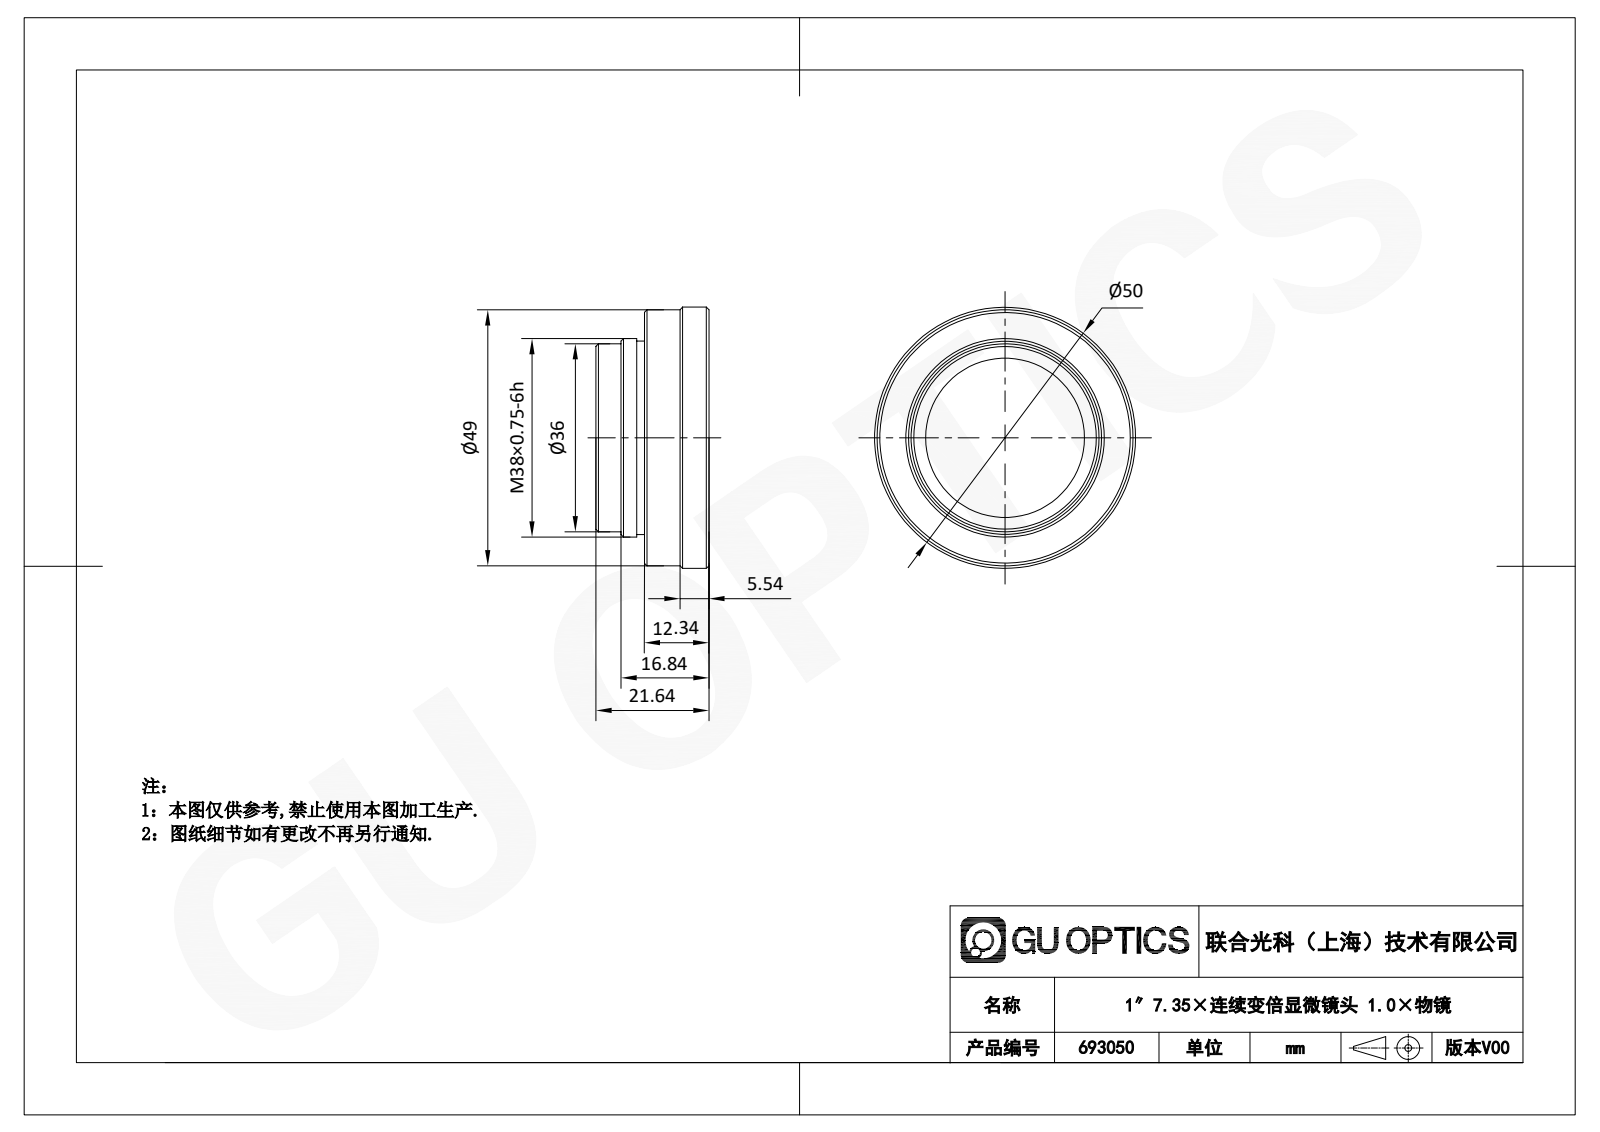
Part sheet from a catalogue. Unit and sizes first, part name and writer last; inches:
Units: inches
Overall size (bounding box): 15.16 × 8.528 × 8.528
Round holes (diameter × count): ⌀1.417 ×1, ⌀1.457 ×1, ⌀1.496 ×1, ⌀1.929 ×1, ⌀1.969 ×1
Round bosses / shafts (diameter × count): ⌀1.732 ×1
Main face-to-face distances: 0.486, 0.852, 0.366, 0.545, 0.059, 0.307, 0.663, 0.177, 0.118, 0.189
Volume: 1 800 in³ · Surface area: 727.5 in²
Bodies: 1 solid, 18 faces (5 planar, 6 cylindrical, 7 other)
Part name (STEP PRODUCT): 693050
STEP written by: SolidWorks 2020 (CONFIG_CONTROL_DESIGN)
